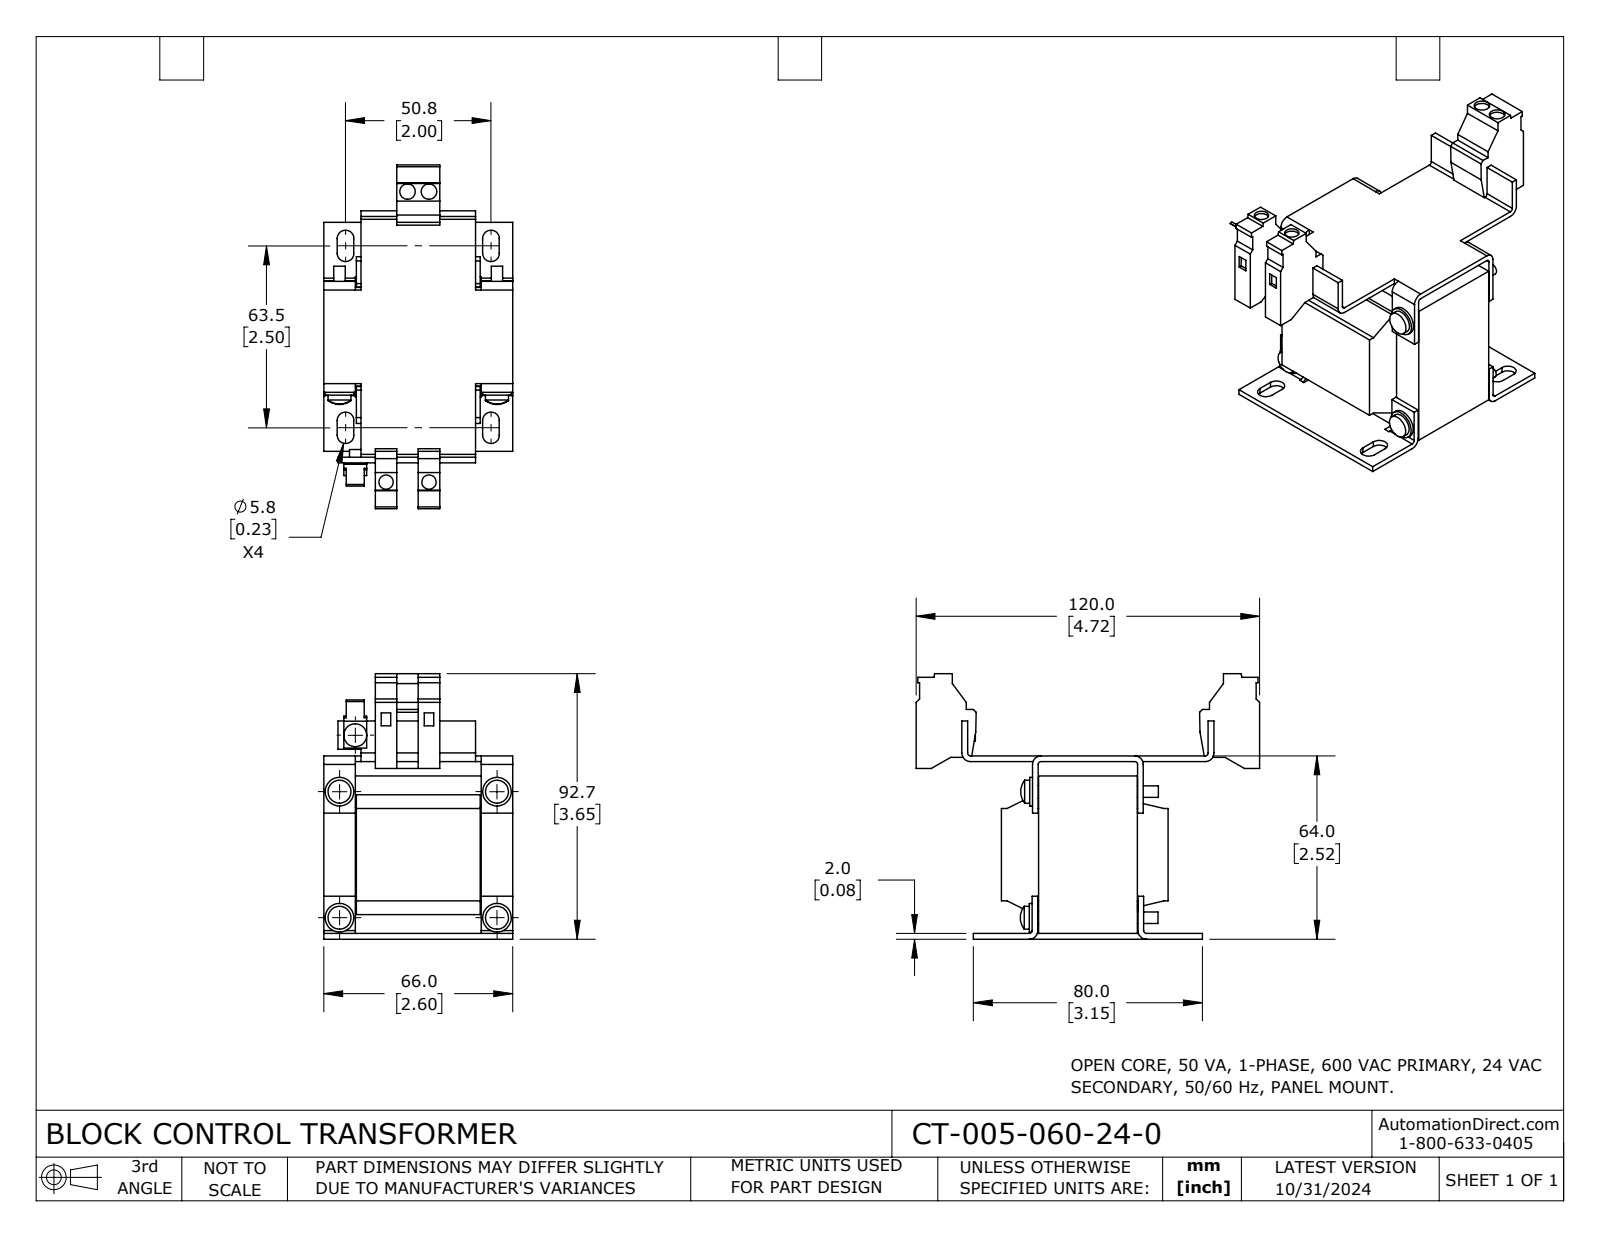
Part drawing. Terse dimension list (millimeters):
name: CT-005-060-24-0
written by: SolidWorks 2023 (CONFIG_CONTROL_DESIGN)
unit: mm
bodies: 1 solid, 326 faces (233 planar, 89 cylindrical, 4 other)
size: 120 × 92.7 × 66
volume: 198 900 mm³; area: 54 990 mm²
holes: 2× ⌀5, 2× ⌀5.4
bosses: 5× ⌀8, 5× ⌀4, 4× ⌀10, 4× ⌀4.5
rounds: 8× R2.9, 6× R1, 6× R3
face distances: 2, 62, 55, 11, 64, 11.4, 54.6, 60, 44, 7
hole spacings: 101.7, 7.5, 15, 101.4, 102.5
